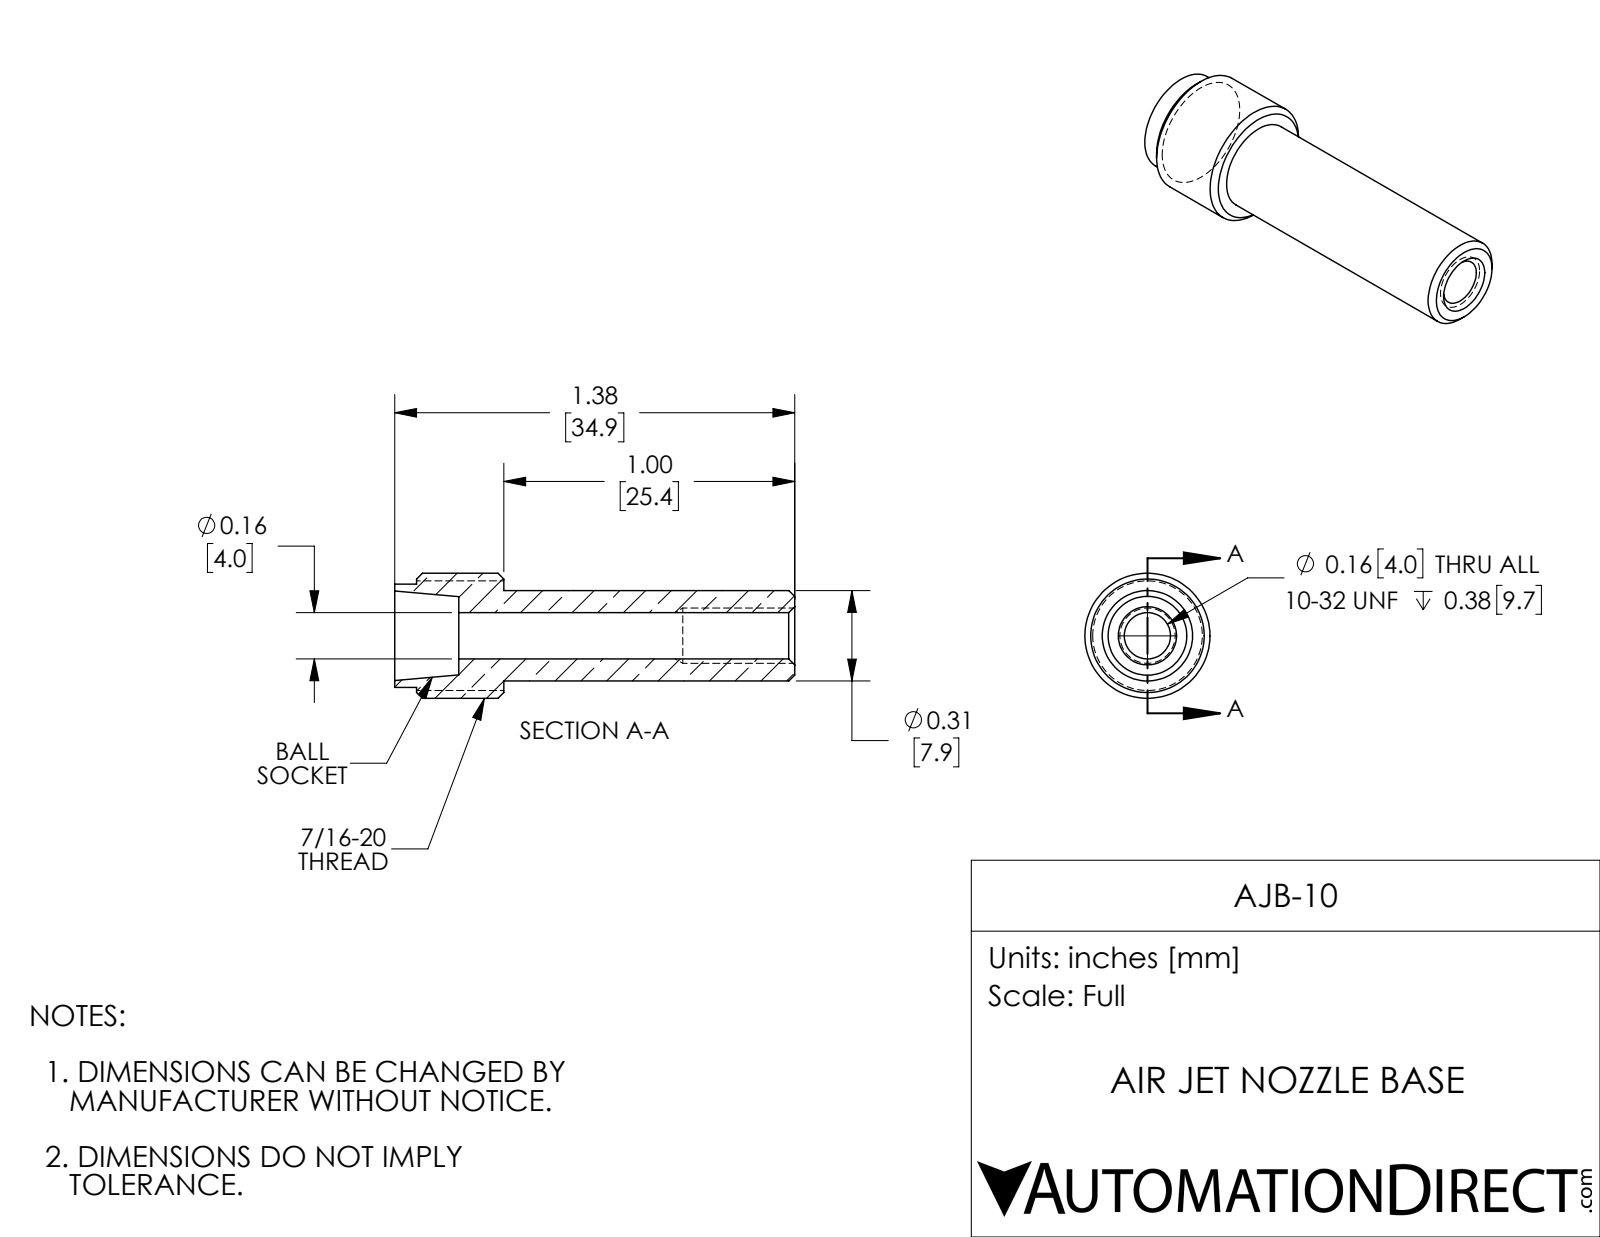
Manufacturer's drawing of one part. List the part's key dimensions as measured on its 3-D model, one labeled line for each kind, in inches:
Part name (STEP PRODUCT): AJB-10
STEP written by: SolidWorks 2018 (AUTOMOTIVE_DESIGN)
Units: inches
Bodies: 1 solid, 23 faces (5 planar, 8 cylindrical, 10 other)
Overall size (bounding box): 1.375 × 0.43 × 0.43
Volume: 0.089 in³ · Surface area: 2.424 in²
Round holes (diameter × count): ⌀0.159 ×1
Round bosses / shafts (diameter × count): ⌀0.43 ×1, ⌀0.355 ×1, ⌀0.31 ×1
Main face-to-face distances: 0.155, 1, 1.155, 1.375, 0.375, 0.22, 1.3, 0.3, 0.145, 0.075
